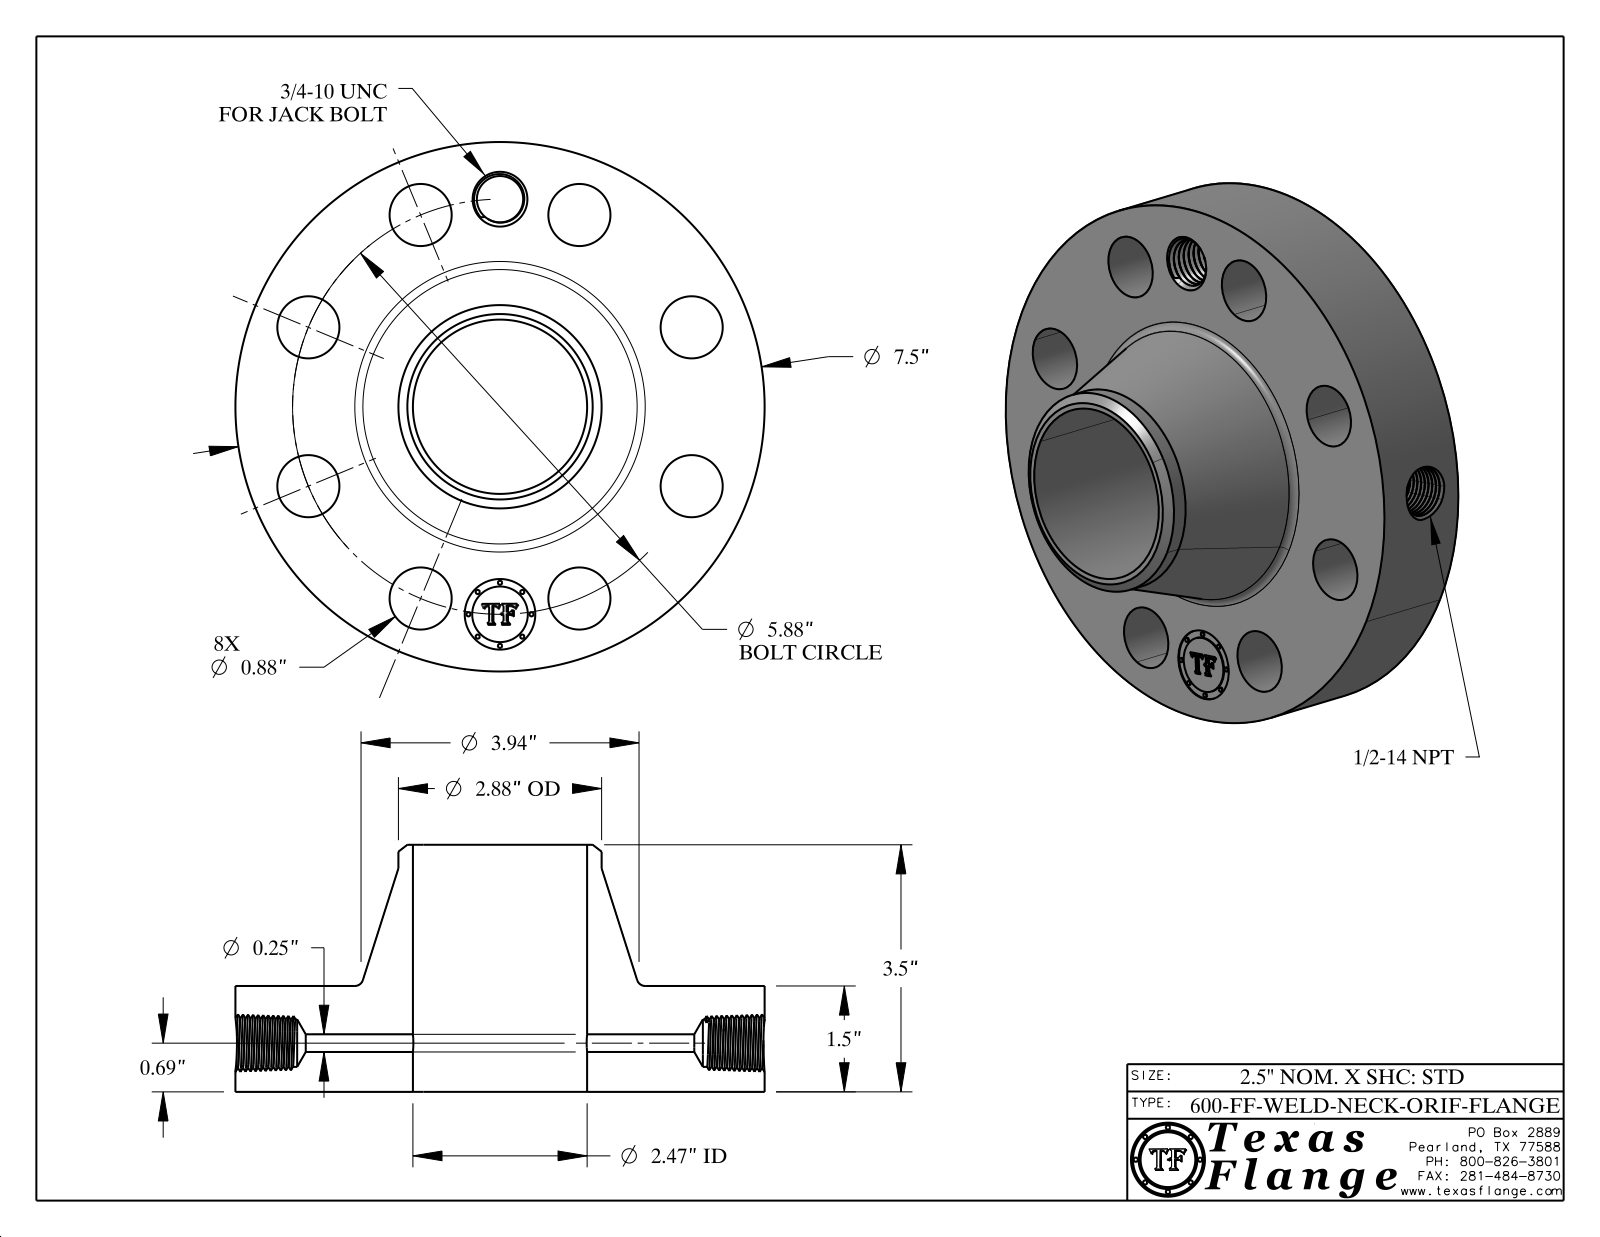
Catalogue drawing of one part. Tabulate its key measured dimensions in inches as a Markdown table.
| quantity | value |
| --- | --- |
| part name | 600-FF-WELD-NECK |
| STEP written by | CATIA V5 STEP AP214 (AUTOMOTIVE_DESIGN) |
| units | inches |
| bodies | 1 solid, 768 faces (368 planar, 90 cylindrical, 310 other) |
| overall size | 7.5 × 7.5 × 3.5 |
| volume | 58.17 in³ |
| surface area | 193 in² |
| round holes (diameter × count) | 0.88 × 8, 0.25 × 1, 0.656 × 1, 0.672 × 1, 1 × 1, 2.469 × 1 |
| round bosses / shafts (diameter × count) | 0.061 × 8, 7.5 × 1, 2.88 × 1, 0.788 × 1 |
| main face-to-face distances | 1.5, 3.5, 2, 0.015, 1.485, 2.015, 0.298, 0.292, 0.054, 0.248 |
| hole center spacings | 2.94, 4.158, 5.432, 1.147, 2.25, 2.25, 3.267, 4.889 |
